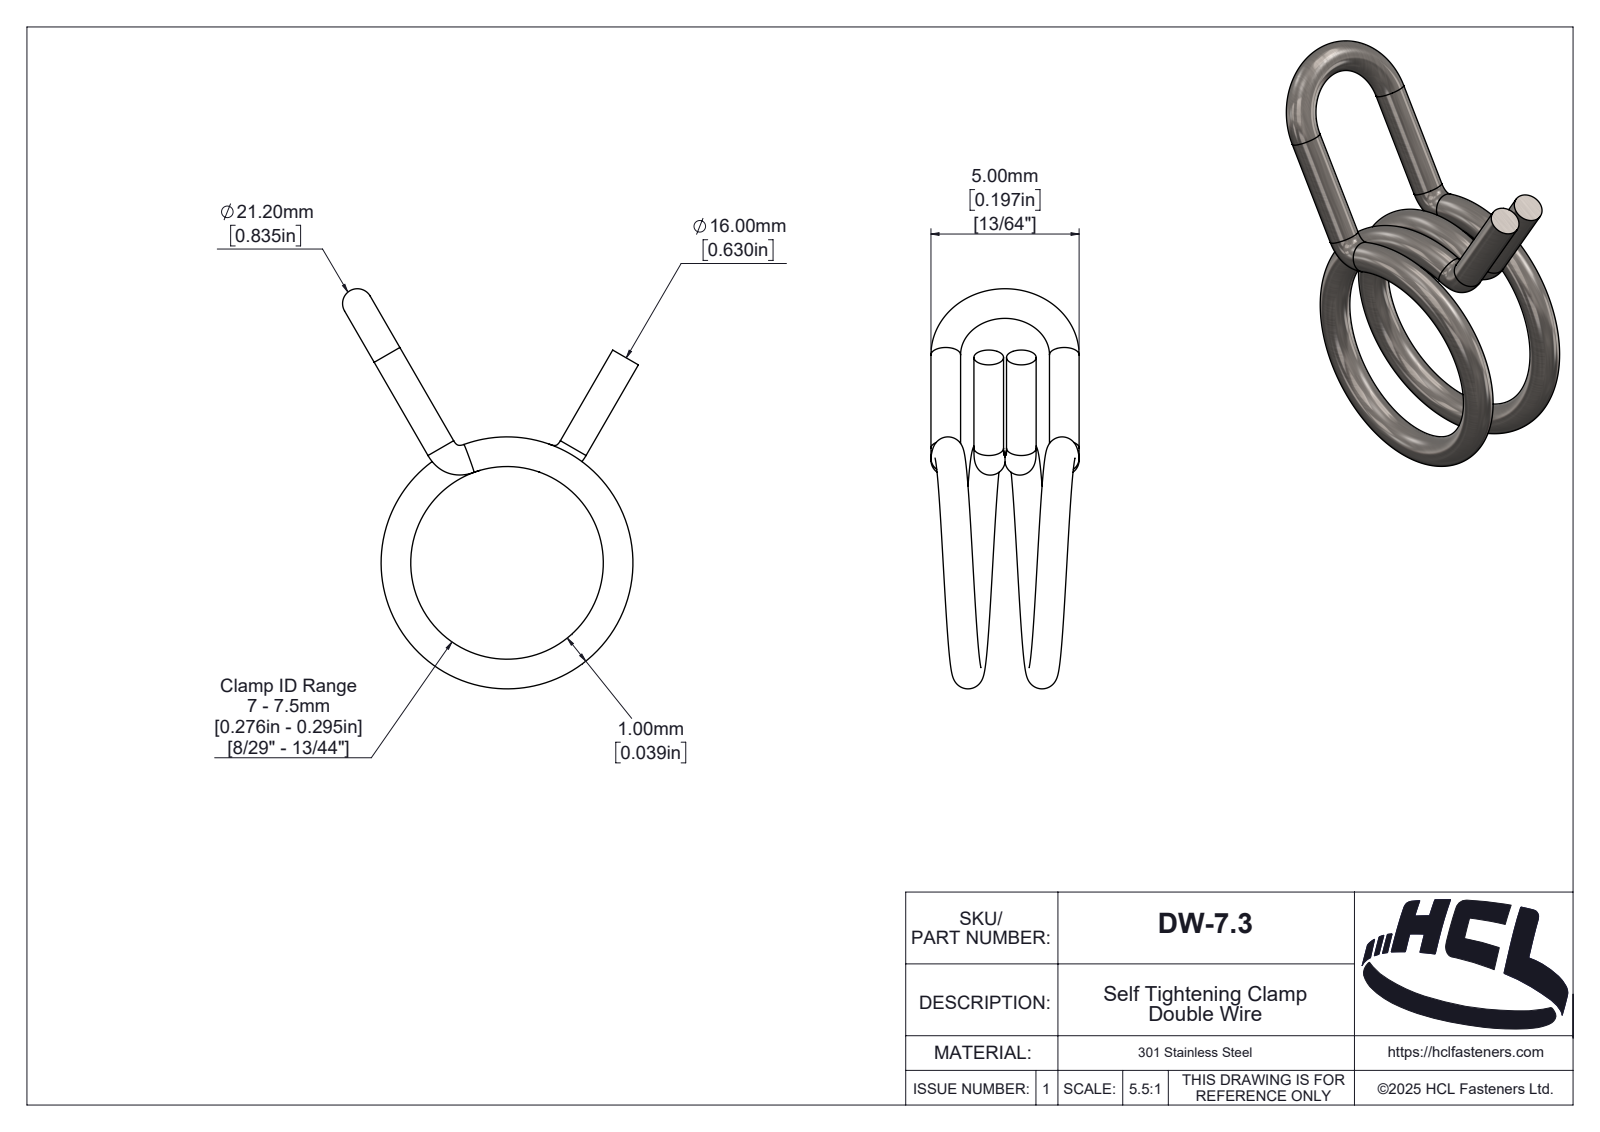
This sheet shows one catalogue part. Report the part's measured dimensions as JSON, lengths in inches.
{"part_name": "DW-7.3", "step_written_by": "SolidWorks 2025 (AUTOMOTIVE_DESIGN)", "units": "inches", "bodies": {"solids": 1, "faces": 125, "planar": 14, "cylindrical": 53, "other": 58}, "overall_size": [0.531, 0.393, 0.197], "volume_in3": 0.004, "surface_area_in2": 0.38, "round_bosses_or_shafts": [[0.039, 4]], "partial_cylinders_radius": [[0.006, 1], [0.008, 1], [0.008, 1], [0.01, 1], [0.014, 1], [0.019, 1], [0.024, 1], [0.027, 1]]}
